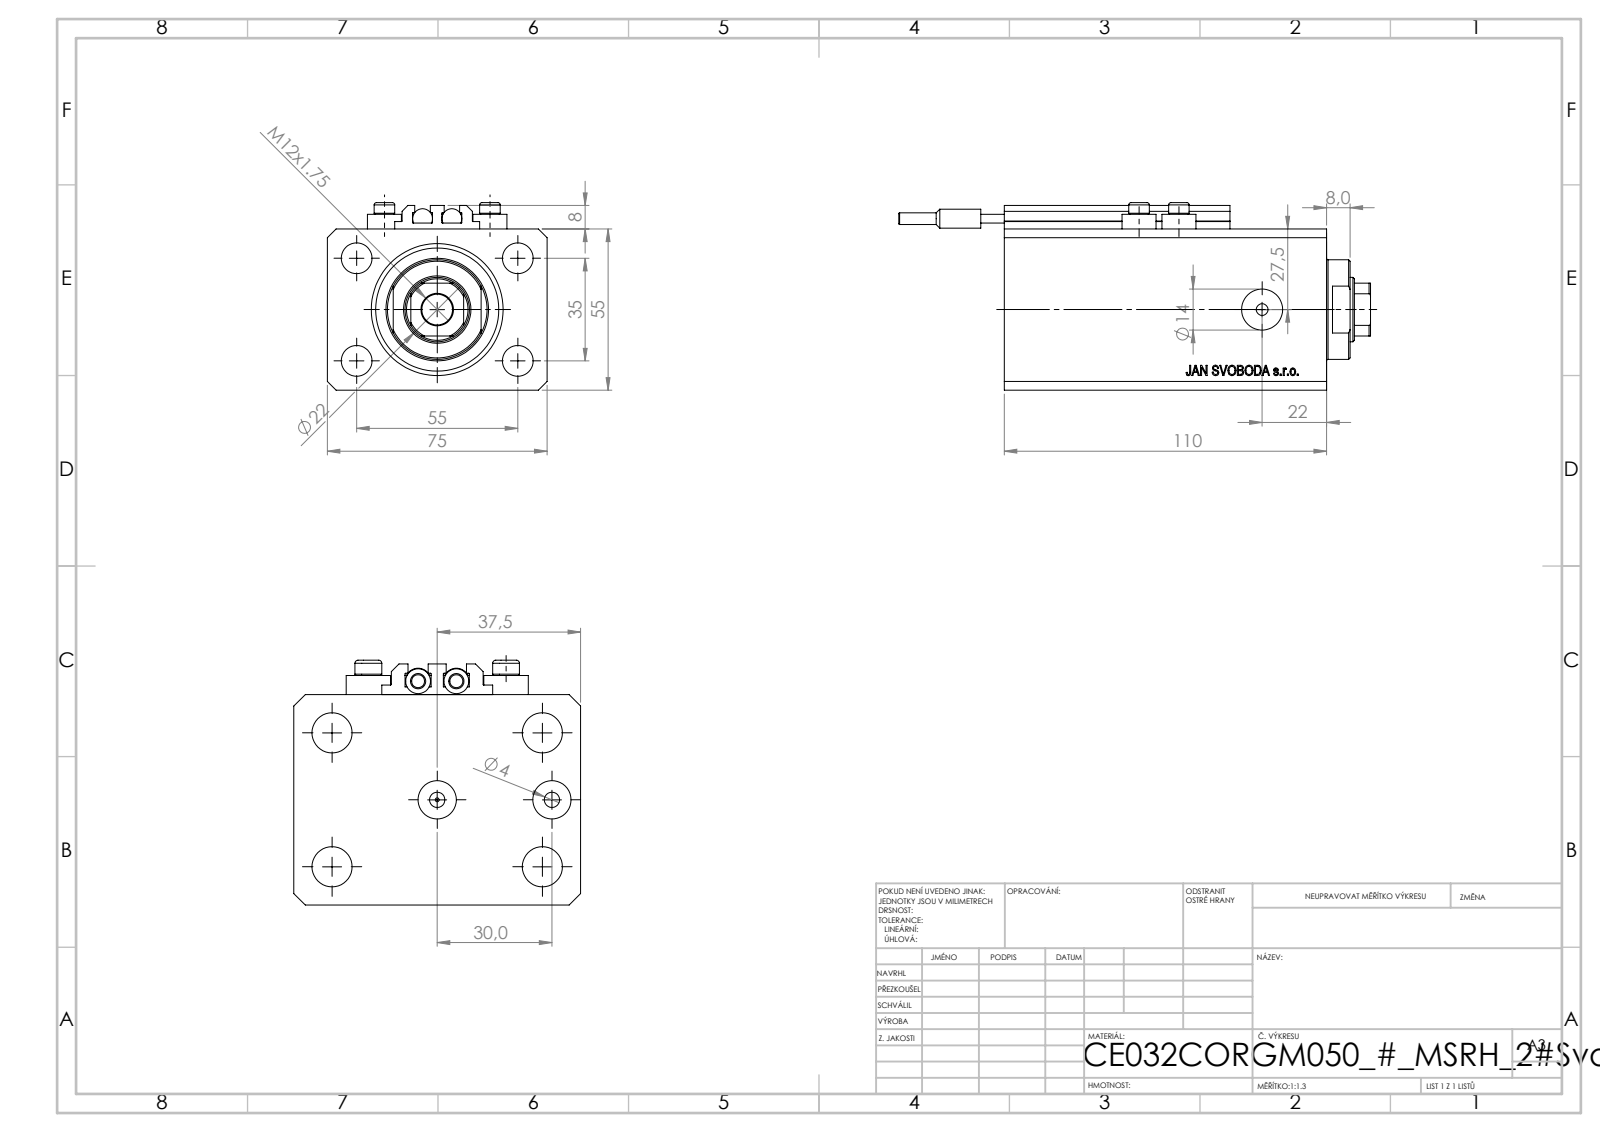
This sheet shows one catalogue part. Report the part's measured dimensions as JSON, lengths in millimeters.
{"part_name": "V250CE_VC_C; ALLEN BOLT V250CE; SWITCH_V250CE; V250CE_C_VCP (+1 more)", "step_written_by": "SolidWorks 2019 (CONFIG_CONTROL_DESIGN)", "units": "millimeters", "bodies": {"solids": 10, "faces": 1090, "planar": 536, "cylindrical": 100, "other": 454}, "overall_size": [161, 75, 64], "volume_mm3": 412020, "surface_area_mm2": 94358, "round_holes": [[4, 8], [10.5, 5], [10, 2], [14, 2], [1.25, 1], [22, 1], [32, 1], [45, 1]], "round_bosses_or_shafts": [[11.6, 4], [7, 4], [6.8, 2], [6.5, 2], [4, 2], [34, 1]], "partial_cylinders_radius": [[0.2, 10], [10.5, 1]], "face_to_face_distances": [55, 75, 110, 15, 95, 3, 9.9, 85.1, 100.1, 2], "hole_center_spacings": [32.6, 13.6, 17.68, 35, 36, 38.48, 55, 60.1]}
